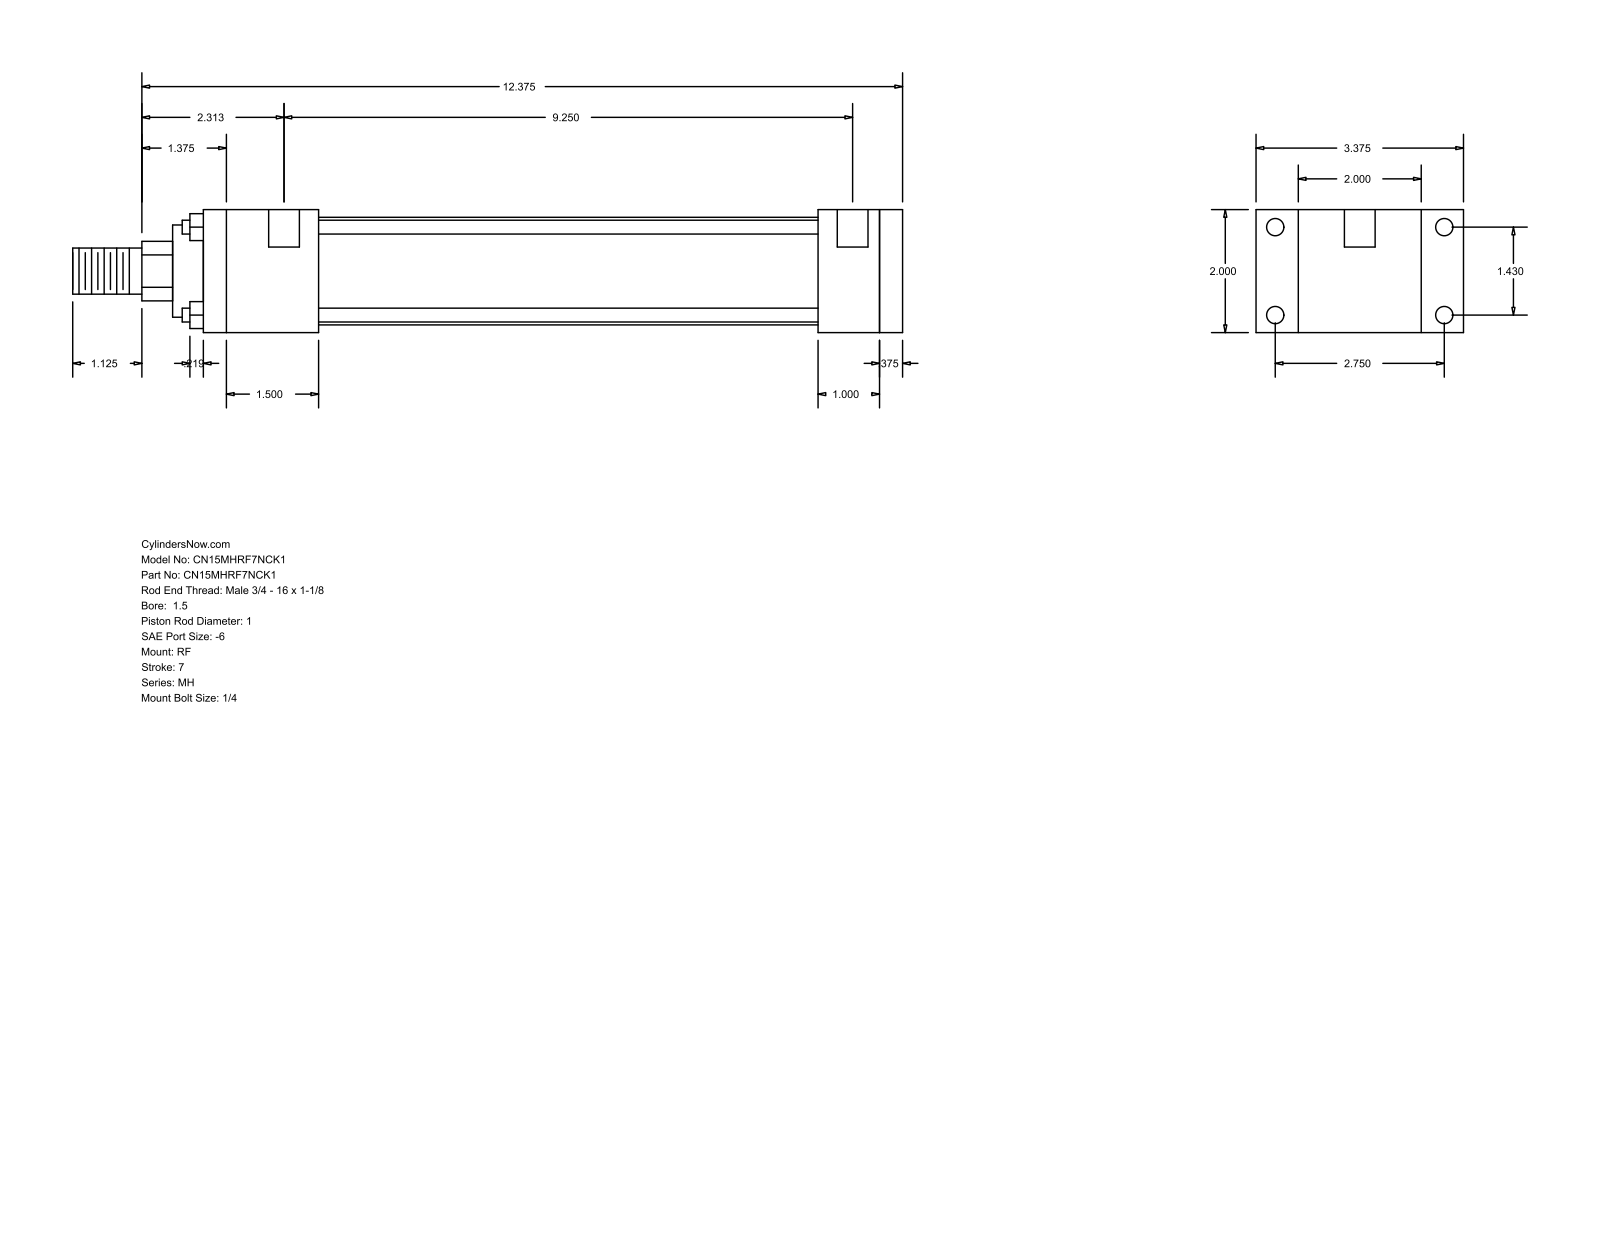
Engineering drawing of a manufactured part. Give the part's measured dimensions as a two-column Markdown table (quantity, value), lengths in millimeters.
| quantity | value |
| --- | --- |
| part name | MH_RF__0150_1 |
| STEP written by | GSSL Pune (CONFIG_CONTROL_DESIGN) |
| units | millimeters |
| bodies | 0 solids, 92 faces (64 planar, 28 cylindrical, 0 other) |
| overall size | 342.9 × 85.72 × 50.8 |
| round holes (diameter × count) | 5.56 × 4, 7.14 × 4, 12.7 × 2 |
| round bosses / shafts (diameter × count) | 5.71 × 4, 44.45 × 1, 38.1 × 1, 25.4 × 1, 19.05 × 1 |
| partial cylindrical surfaces (radius × count) | 12.29 × 1 |
| main face-to-face distances | 50.8, 9.52, 279.4, 25.4, 288.92, 17.46, 68.26, 254, 34.92, 47.63 |
| hole center spacings | 36.32, 69.84, 78.72, 238.13, 3.18, 234.95 |
